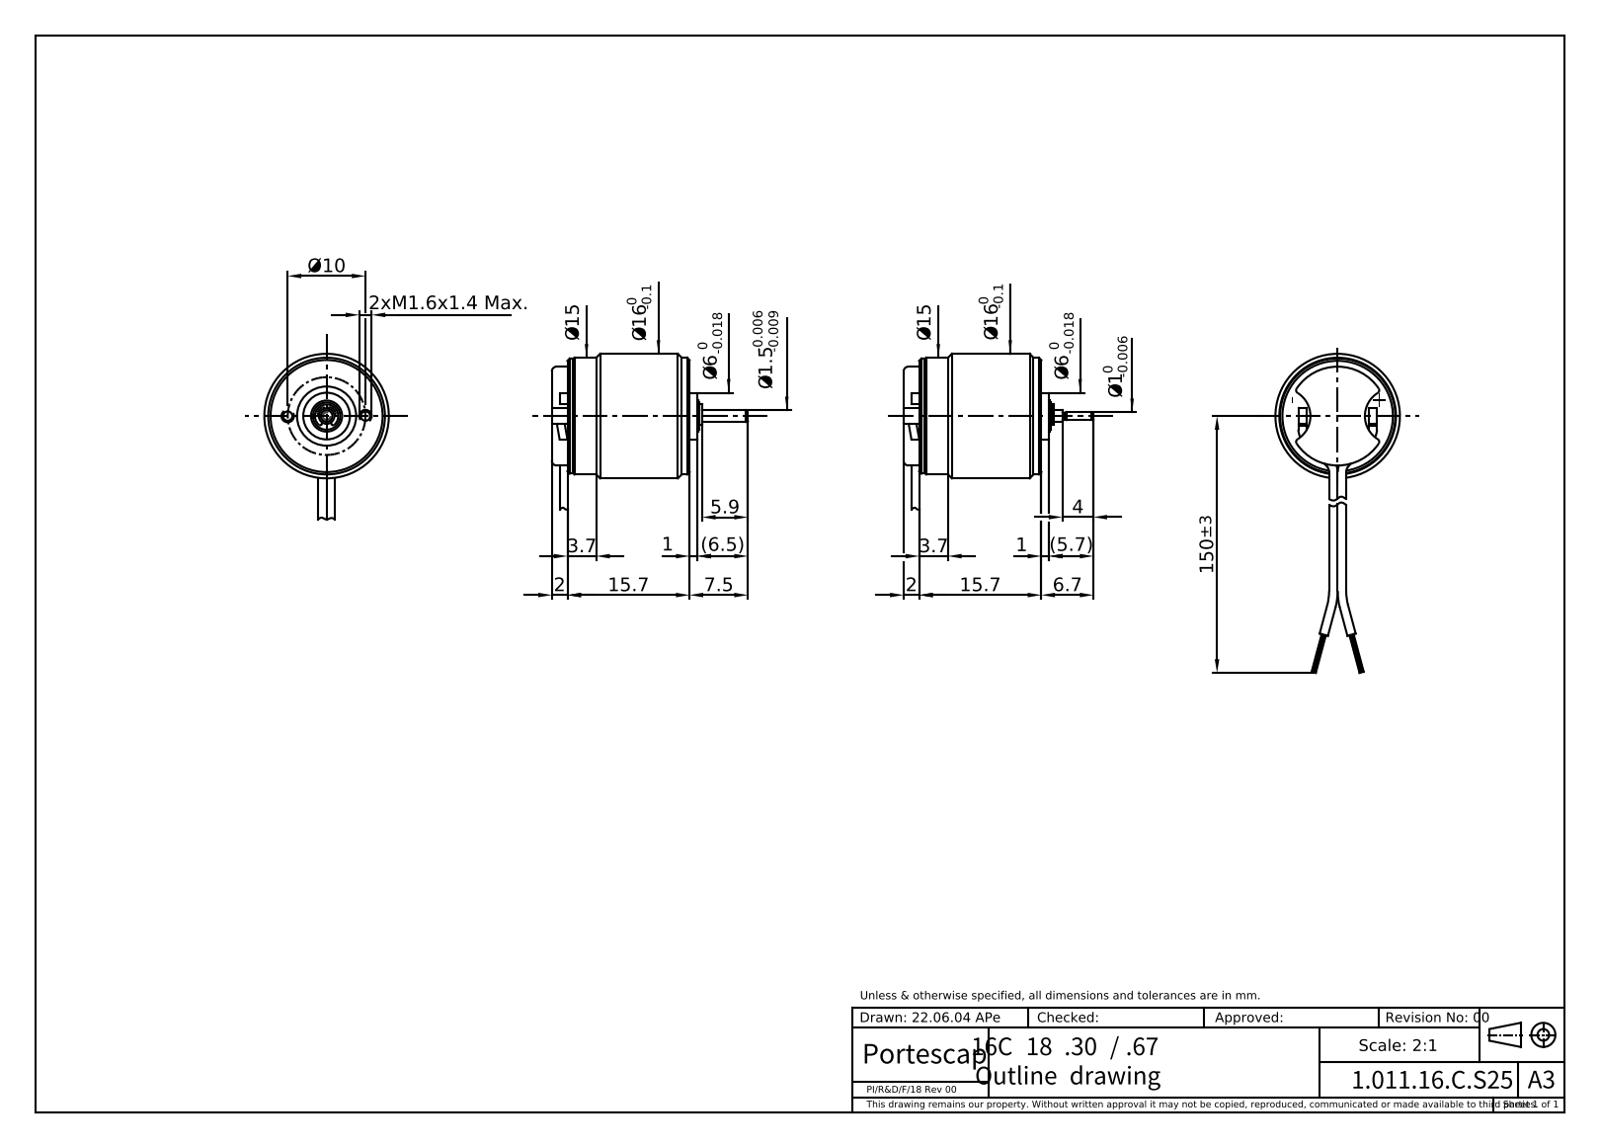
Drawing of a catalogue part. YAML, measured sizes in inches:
part_name: "16C_67"
step_written_by: "PRO/ENGINEER BY PARAMETRIC TECHNOLOGY CORPORATION, 2014310 (CONFIG_CONTROL_DESIGN)"
units: inches
bodies: {solids: 2, faces: 254, planar: 84, cylindrical: 96, other: 74}
overall_size: [1.957, 0.961, 0.63]
volume: 0.199
surface_area: 2.773
round_holes:
  - {diameter: 0.049, count: 2}
  - {diameter: 0.063, count: 2}
round_bosses_or_shafts:
  - {diameter: 0.043, count: 8}
  - {diameter: 0.022, count: 2}
  - {diameter: 0.02, count: 2}
  - {diameter: 0.63, count: 1}
  - {diameter: 0.591, count: 1}
  - {diameter: 0.583, count: 1}
  - {diameter: 0.236, count: 1}
  - {diameter: 0.157, count: 1}
partial_cylinders:
  - {radius: 0.016, count: 8}
  - {radius: 0.008, count: 2}
  - {radius: 0.01, count: 2}
  - {radius: 0.018, count: 2}
  - {radius: 0.02, count: 2}
  - {radius: 0.024, count: 2}
  - {radius: 0.138, count: 2}
  - {radius: 0.165, count: 2}
face_to_face_distances: [0.618, 0.079, 0.697, 0.035, 0.043, 0.661, 0.031, 0.266, 0.039, 0.657]
hole_center_spacings: [0.394]
